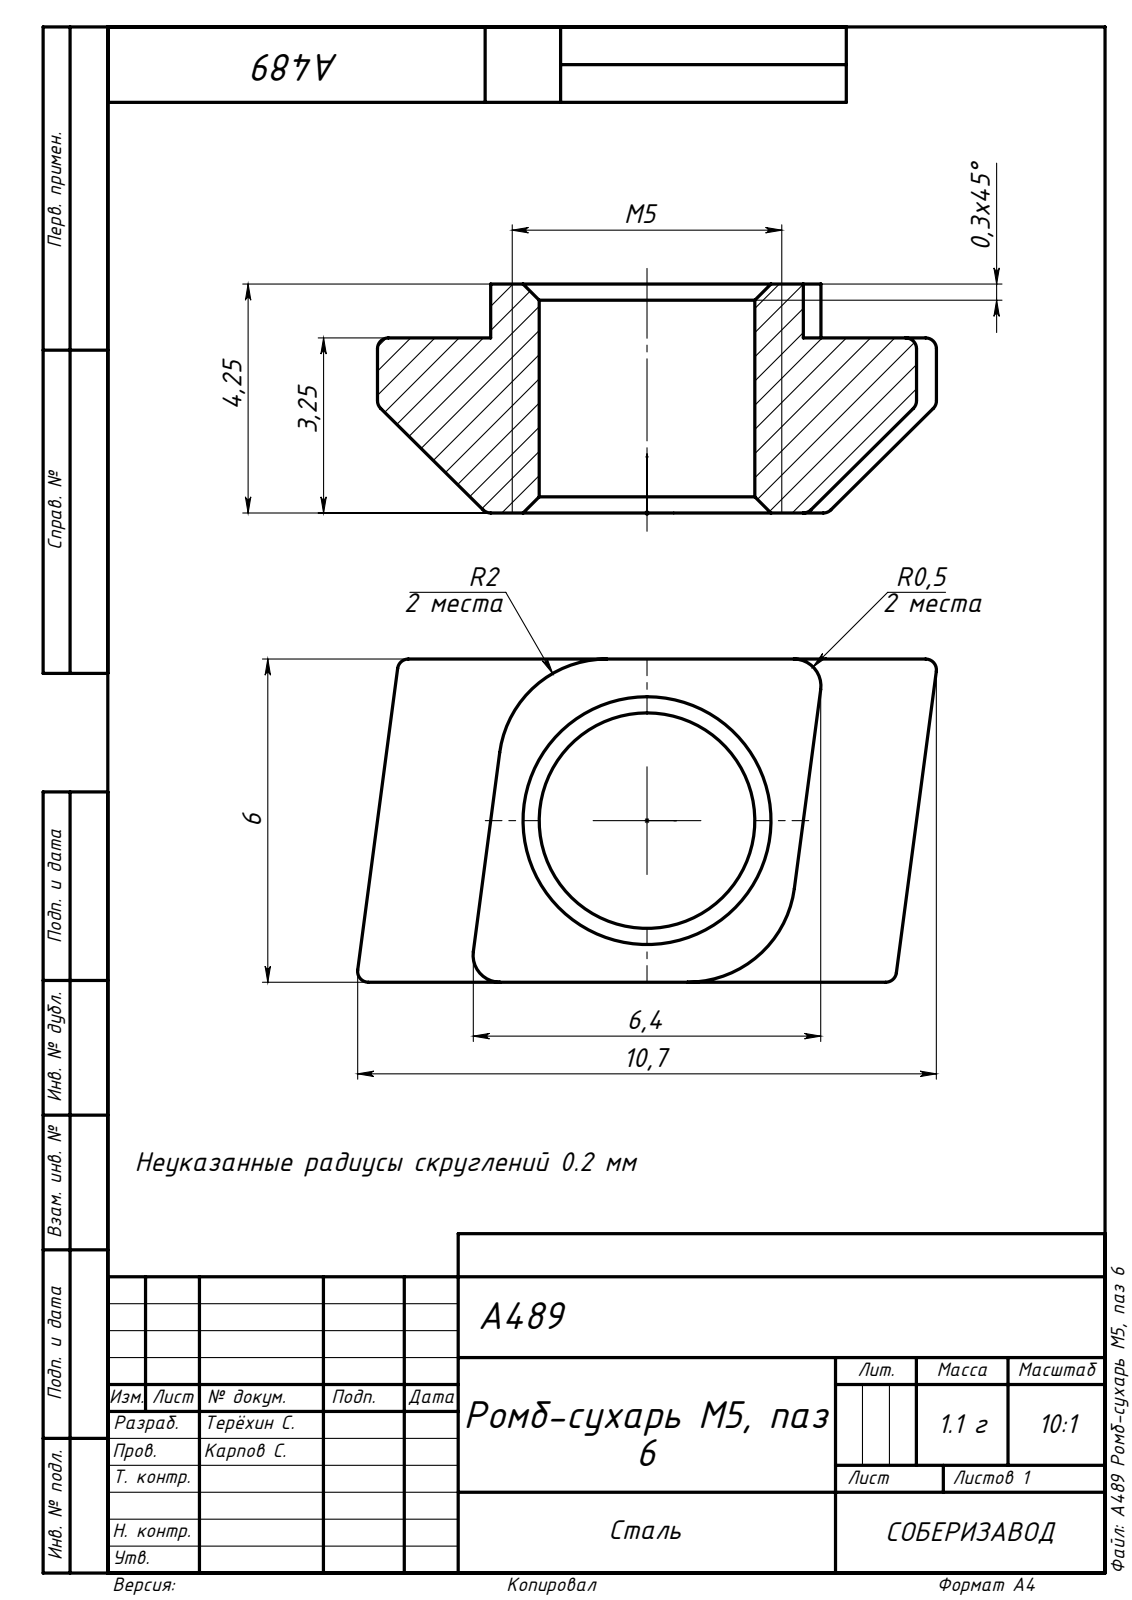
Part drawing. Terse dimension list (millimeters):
name: A489 Ромб-сухарь М5, паз 6
written by: SolidWorks 2021 (AUTOMOTIVE_DESIGN)
unit: mm
bodies: 1 solid, 56 faces (12 planar, 27 cylindrical, 17 other)
size: 10.74 × 6 × 4.25
volume: 149 mm³; area: 243 mm²
holes: 1× ⌀4
rounds: 18× R0.2, 2× R0.5, 2× R2
face distances: 6, 1, 3.25, 4.25, 2.09, 7.83, 9.92, 5.74
